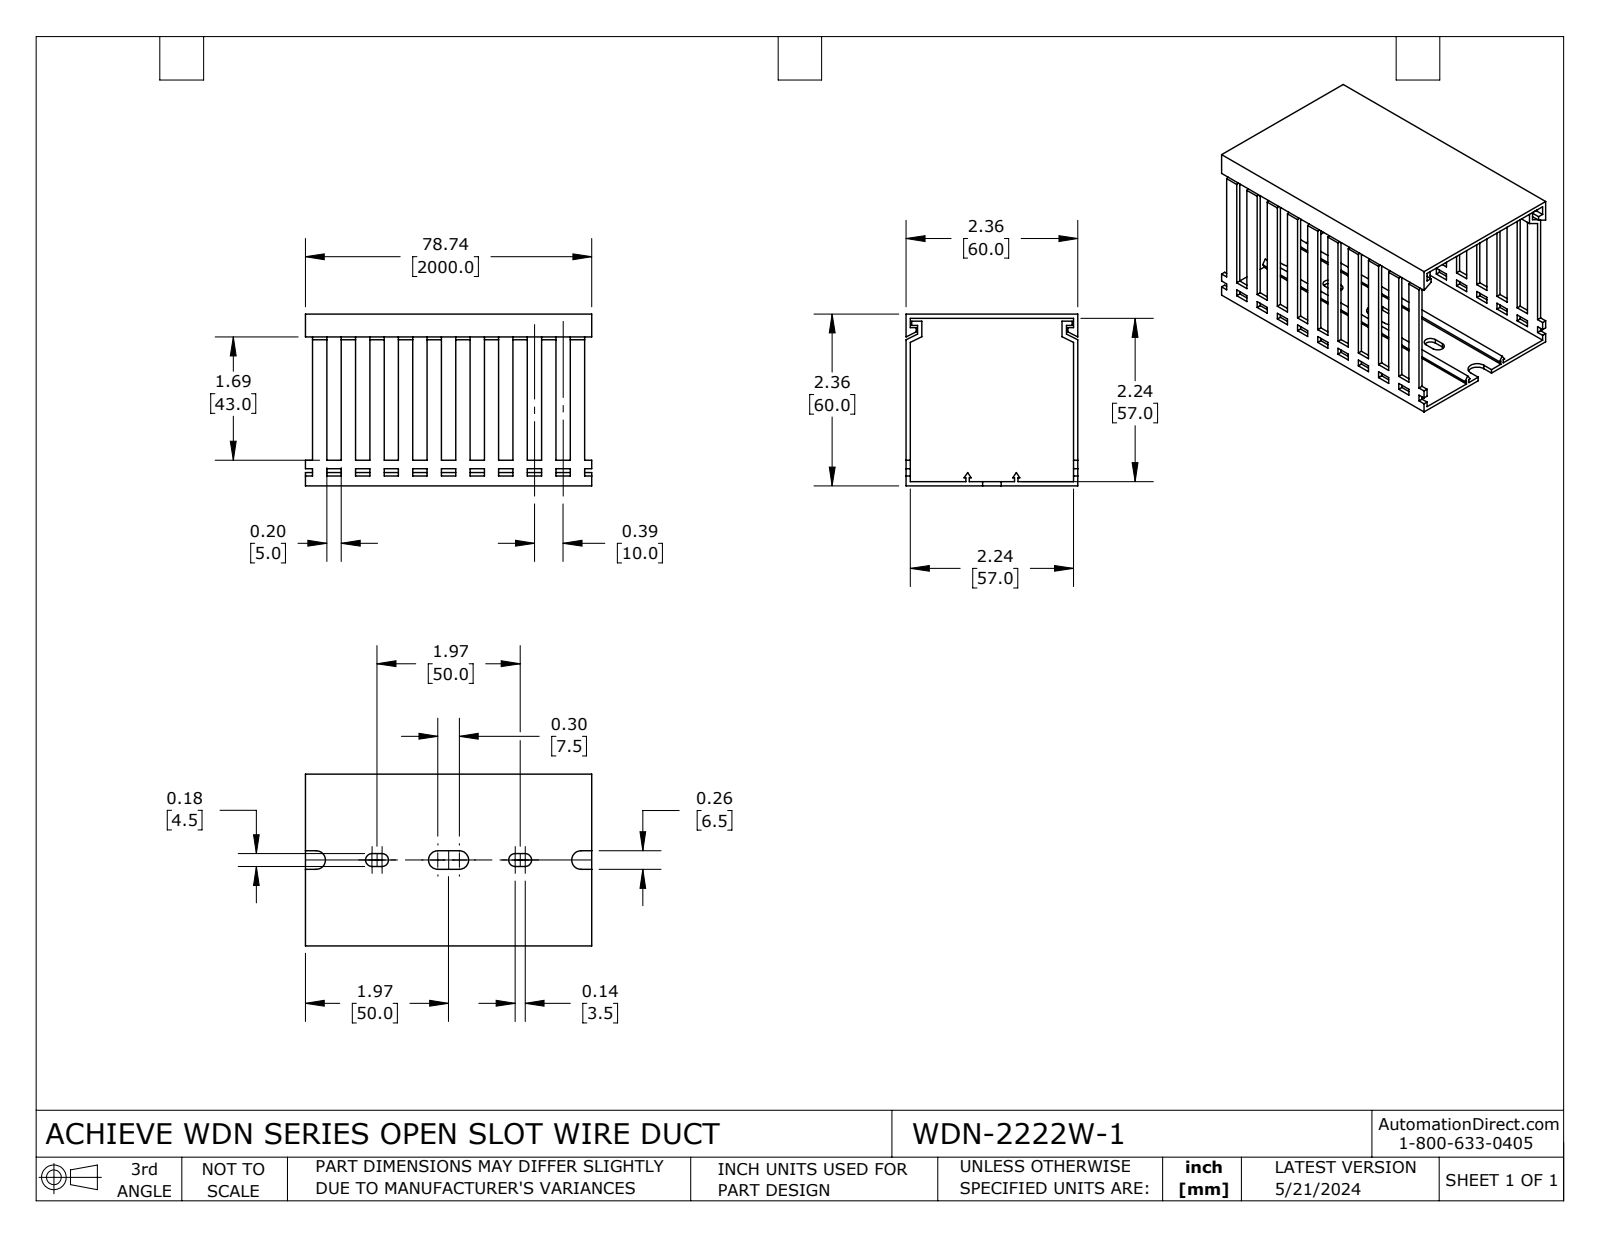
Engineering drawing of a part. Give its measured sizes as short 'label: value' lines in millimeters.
name: WDN-2222W-1
written by: SolidWorks 2023 (CONFIG_CONTROL_DESIGN)
unit: mm
bodies: 2 solids, 350 faces (338 planar, 12 cylindrical, 0 other)
size: 100 × 60 × 60
volume: 30 890 mm³; area: 46 040 mm²
rounds: 4× R2.3, 4× R3.3
face distances: 1.5, 58.5, 60, 57, 10, 5, 15, 20, 25, 30
